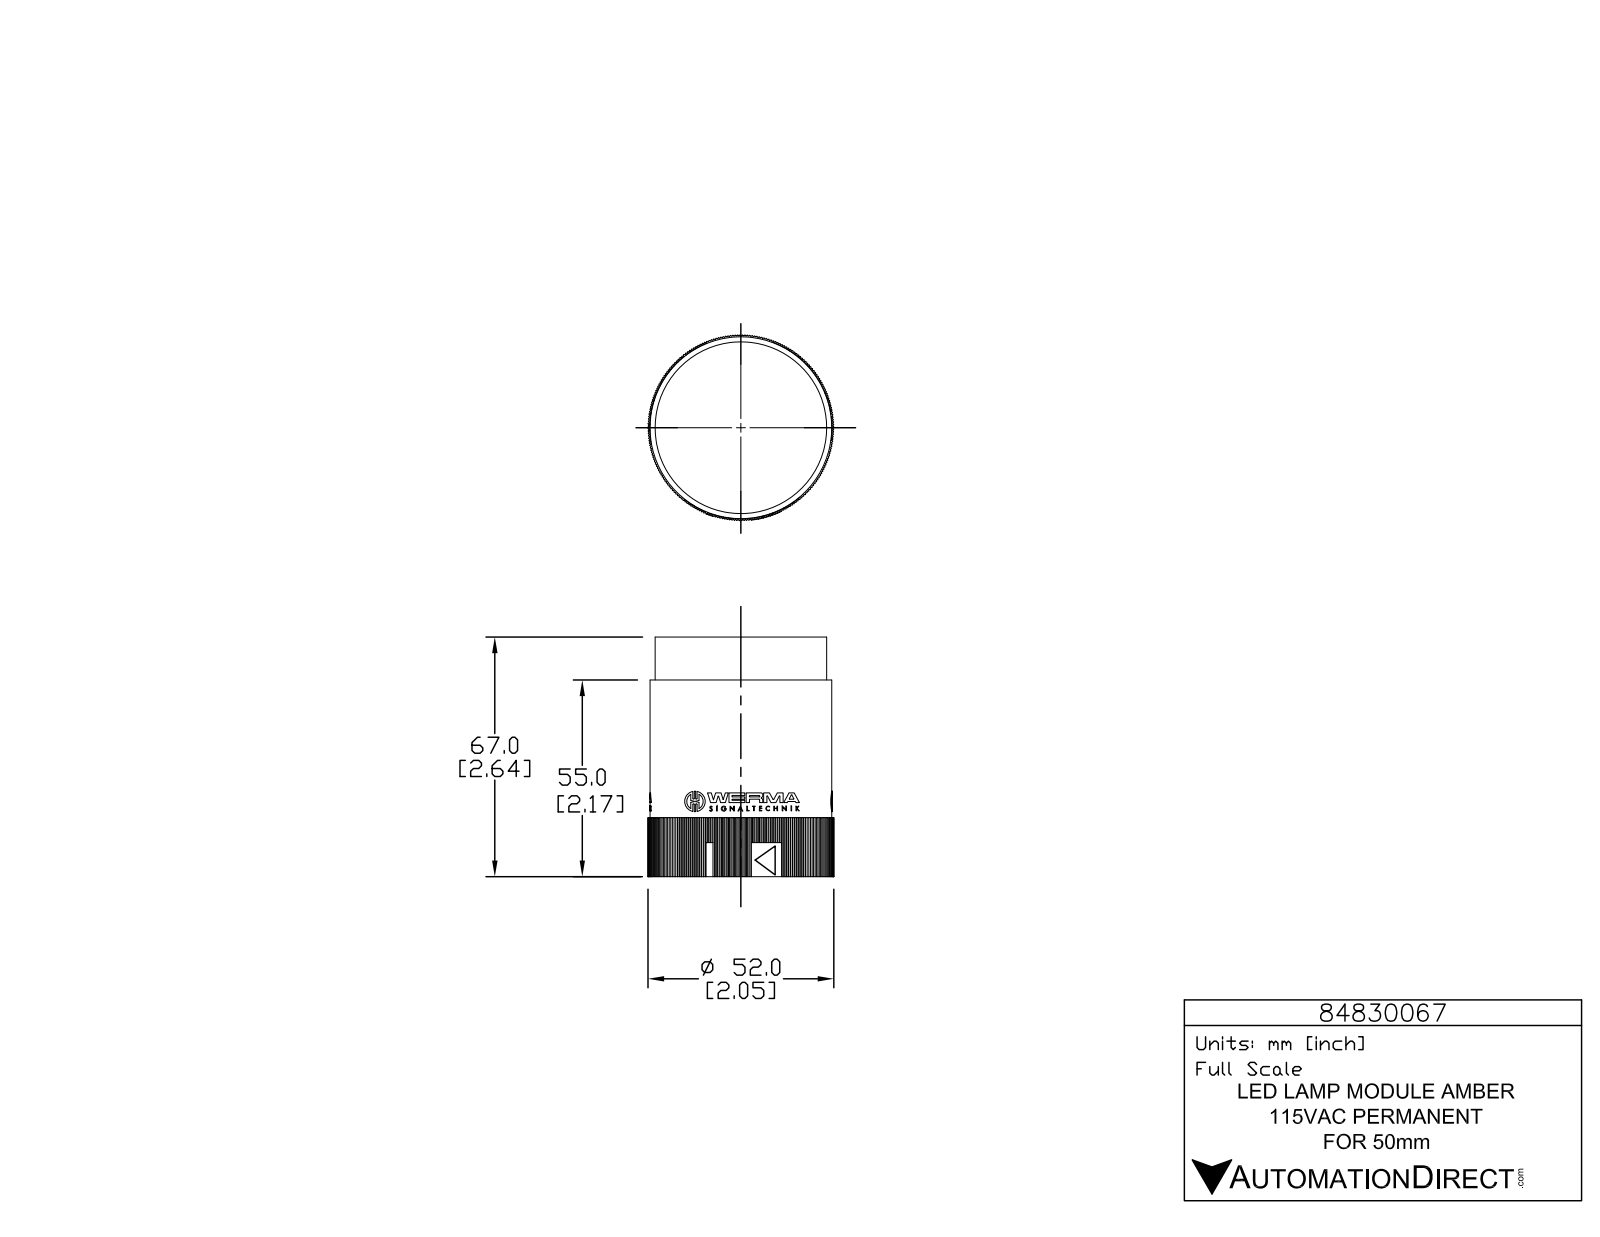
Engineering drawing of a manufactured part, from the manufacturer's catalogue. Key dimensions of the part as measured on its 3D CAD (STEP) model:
Part name (STEP PRODUCT): 84830067
STEP written by: SolidWorks 2015 (AUTOMOTIVE_DESIGN)
Units: inches
Bodies: 1 solid, 1265 faces (1020 planar, 245 cylindrical, 0 other)
Overall size (bounding box): 2.638 × 2.047 × 2.047
Volume: 6.873 in³ · Surface area: 27.62 in²
Round holes (diameter × count): ⌀0.039 ×3, ⌀1.898 ×1
Round bosses / shafts (diameter × count): ⌀0.226 ×3, ⌀0.056 ×3, ⌀2.002 ×1, ⌀1.89 ×1
Partial cylindrical surfaces — rounded edges, fillets, slot ends (radius × count): R0.008 ×6, R0.008 ×6, R0.008 ×6, R0.131 ×6, R0.004 ×3, R0.005 ×3, R0.008 ×3, R0.008 ×3
Main face-to-face distances: 2.165, 1.428, 1.429, 1.429, 0.472, 2.638, 1.428, 1.428, 1.693, 1.988
